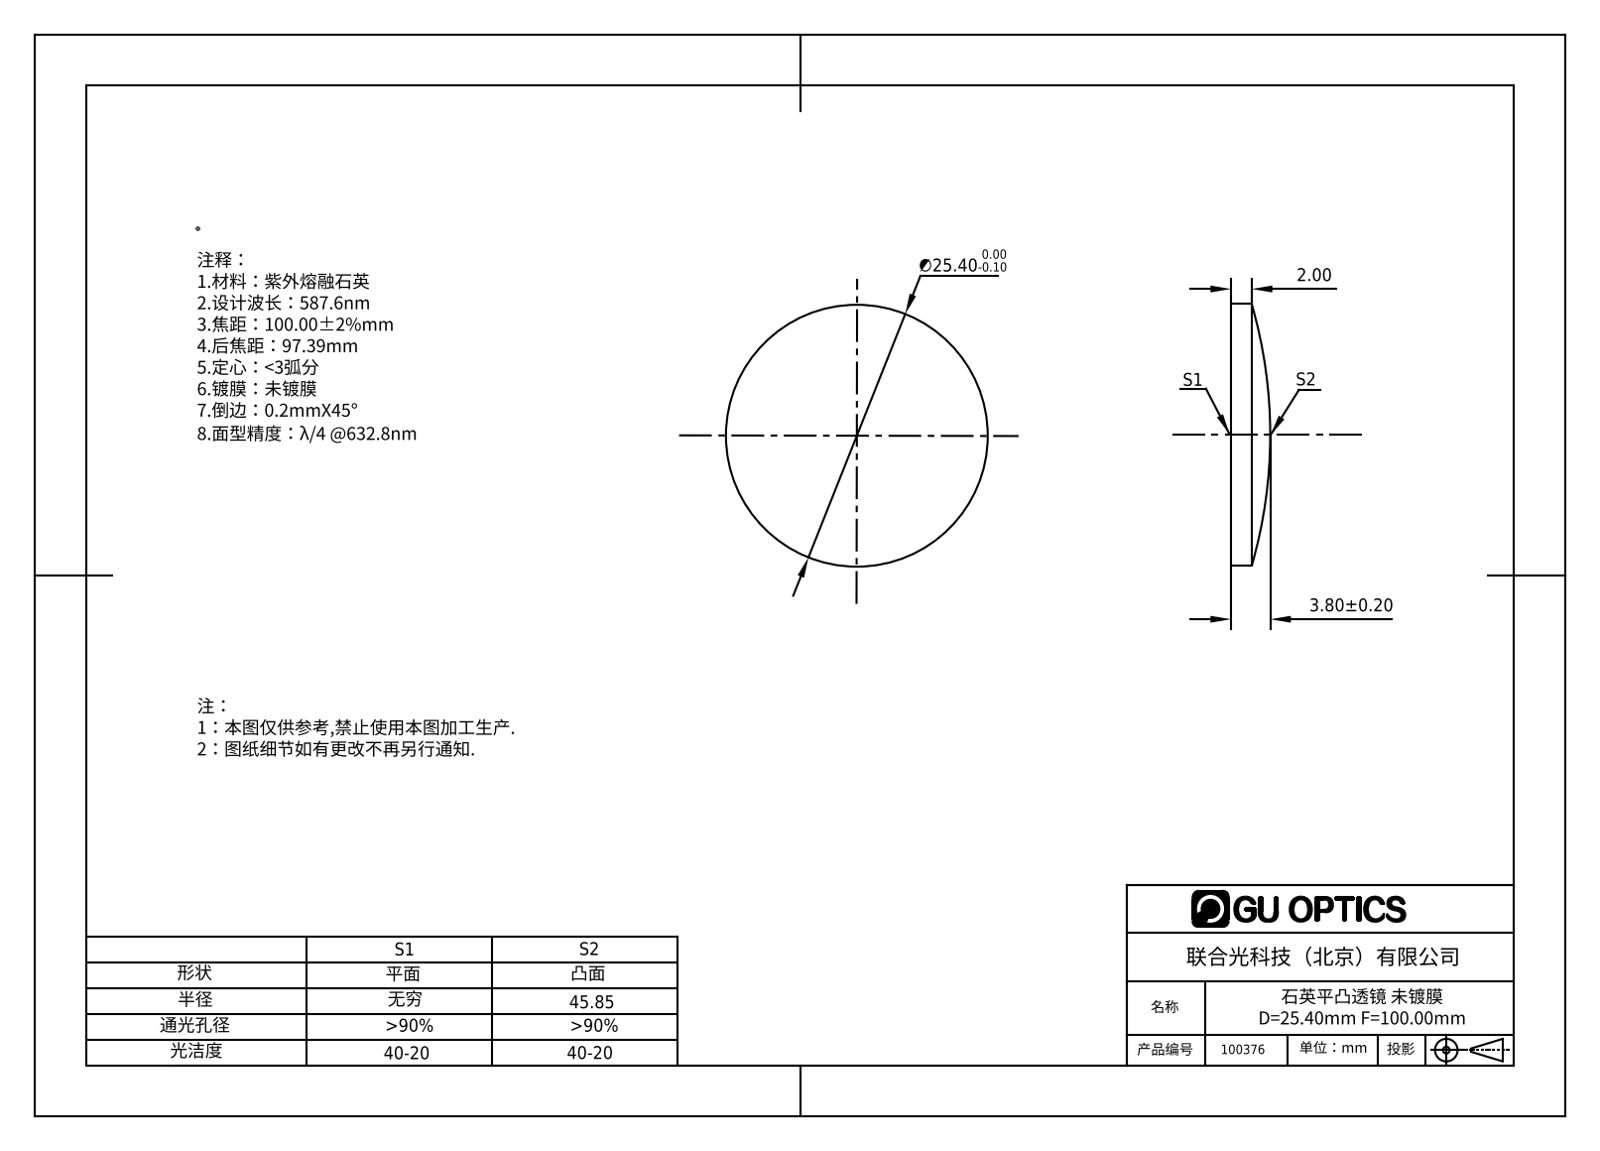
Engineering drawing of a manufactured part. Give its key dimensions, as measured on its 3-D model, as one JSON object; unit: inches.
{"part_name": "100376", "step_written_by": "SolidWorks 2016 (AUTOMOTIVE_DESIGN)", "units": "inches", "bodies": {"solids": 1, "faces": 5, "planar": 1, "cylindrical": 2, "other": 2}, "overall_size": [1, 1, 0.15], "volume_in3": 0.09, "surface_area_in2": 1.834, "round_bosses_or_shafts": [[1, 1]]}
